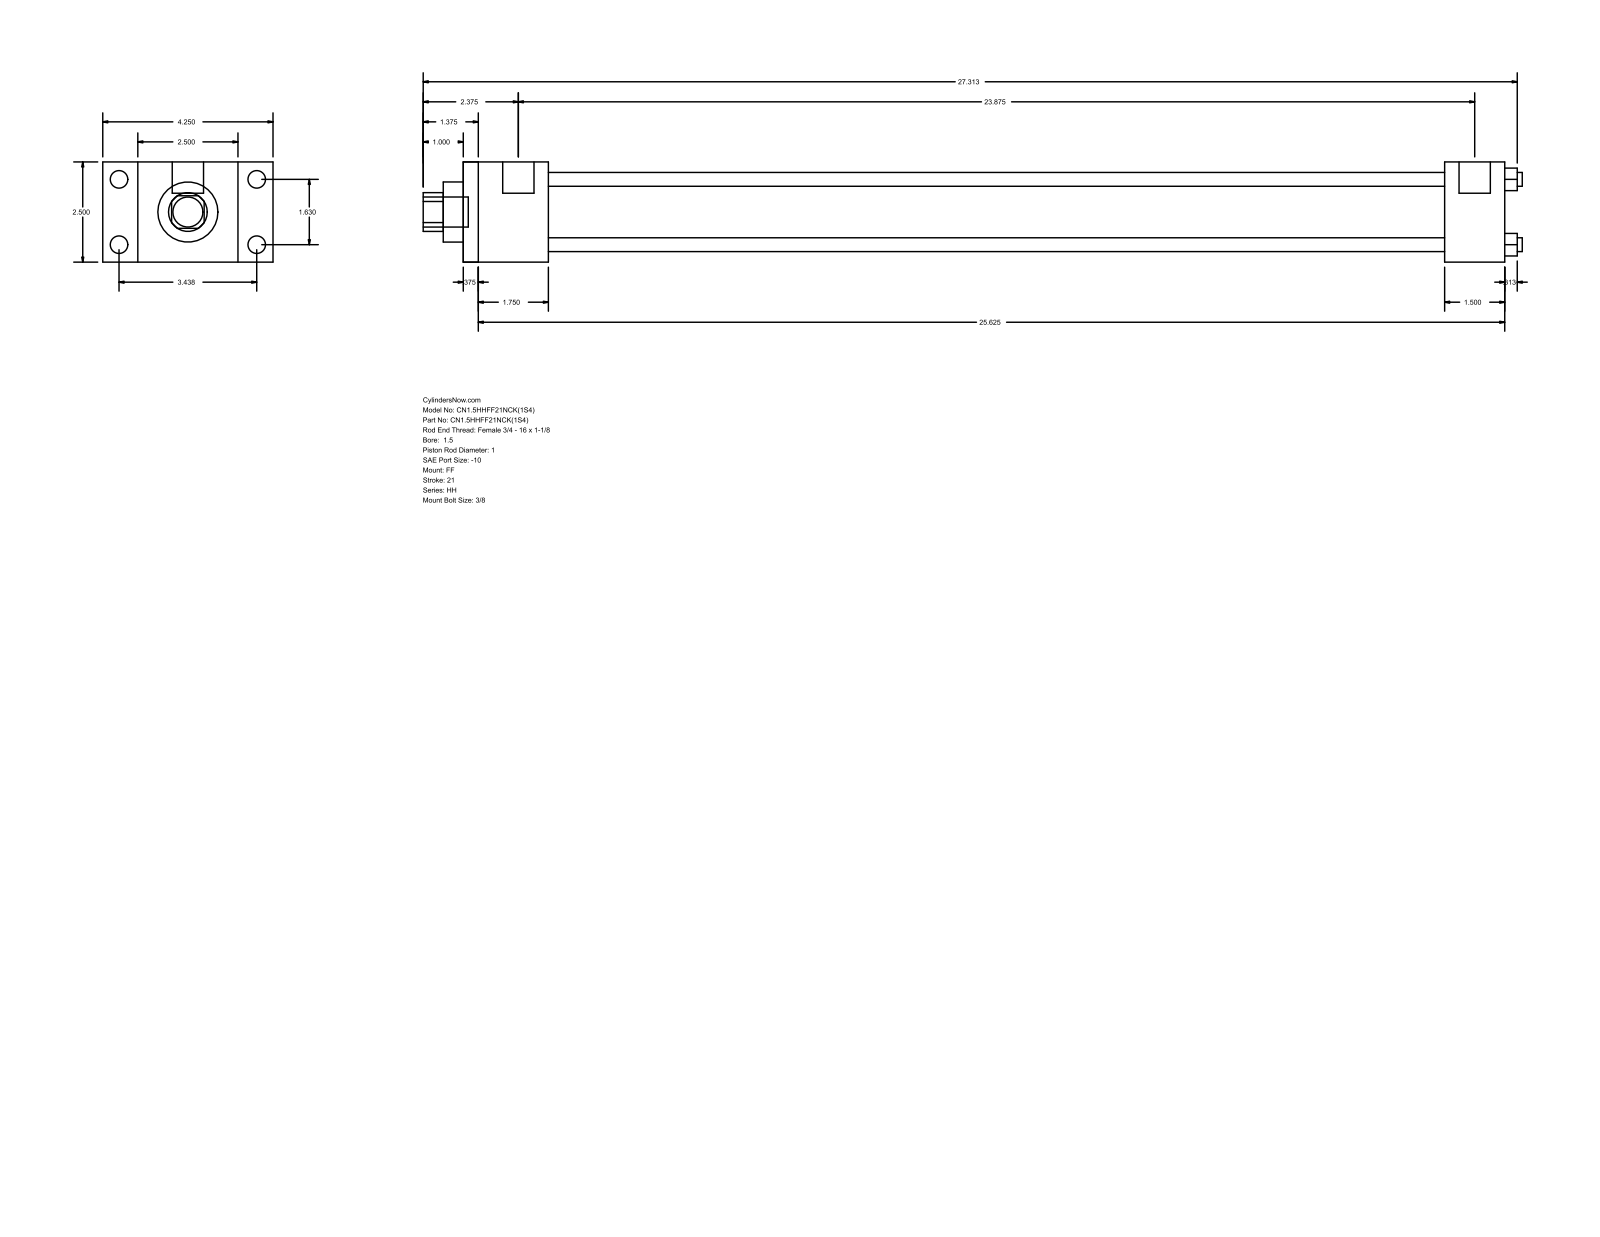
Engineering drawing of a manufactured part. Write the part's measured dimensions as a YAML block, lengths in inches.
part_name: "HH_FF__0150_1"
step_written_by: "GSSL Pune (CONFIG_CONTROL_DESIGN)"
units: inches
bodies: {solids: 0, faces: 92, planar: 64, cylindrical: 28, other: 0}
overall_size: [27.437, 4.25, 2.5]
round_holes:
  - {diameter: 0.345, count: 4}
  - {diameter: 1, count: 1}
  - {diameter: 1.5, count: 1}
  - {diameter: 1.75, count: 1}
round_bosses_or_shafts:
  - {diameter: 0.438, count: 4}
  - {diameter: 0.219, count: 4}
  - {diameter: 0.781, count: 2}
  - {diameter: 0.75, count: 1}
partial_cylinders:
  - {radius: 0.484, count: 1}
face_to_face_distances: [2.5, 26, 0.375, 25.625, 2.125, 1.75, 23.875, 24.5, 24.125, 22.375]
hole_center_spacings: [1.152, 1.63, 2.305]
